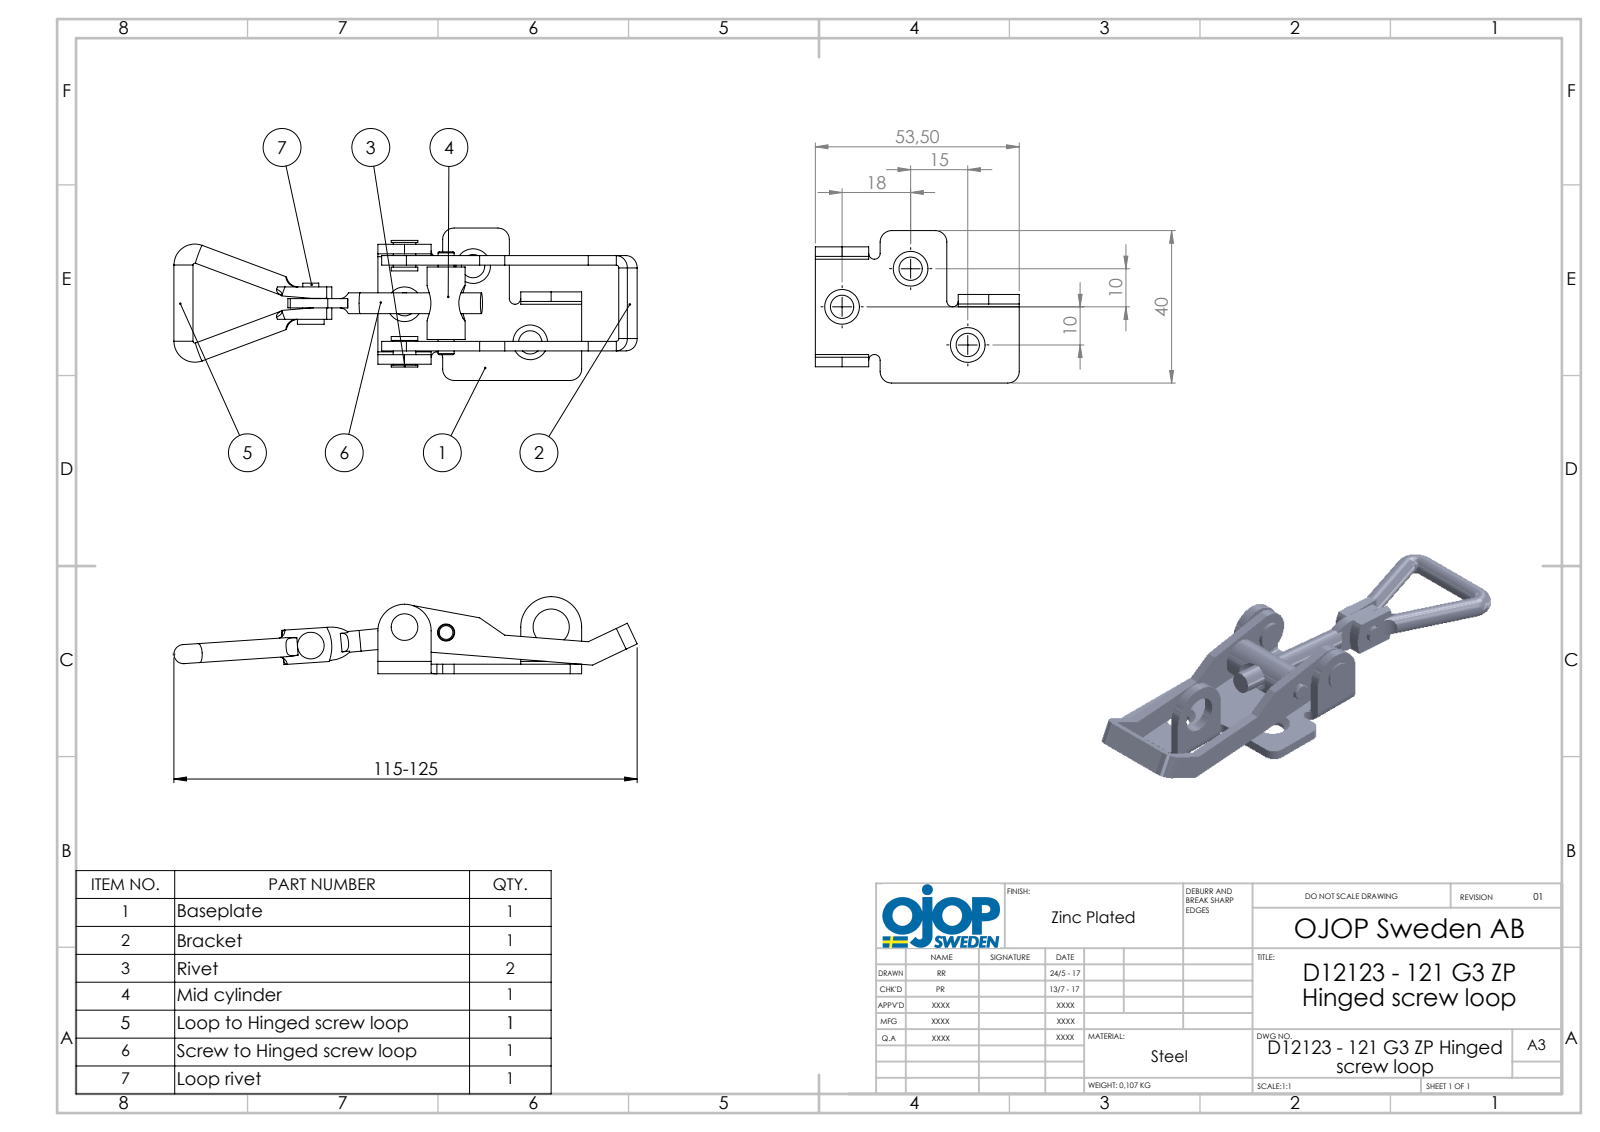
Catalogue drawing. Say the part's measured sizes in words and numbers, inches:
The part is named "bygel; nit; Platta; rulle (+5 more)". Its 3-D file was written by "SolidWorks 2015 (AUTOMOTIVE_DESIGN)". It is 8 solids with 248 faces: 100 planar, 104 cylindrical and 44 other. Overall it measures 4.827 by 1.575 by 0.797 inches. Its volume is 0.836 cubic inches and its surface area 20.86 square inches. Round holes: 3 of diameter 0.217, 3 of diameter 0.236, 2 of diameter 0.177, 1 of diameter 0.197, 1 of diameter 0.374. Round bosses or shafts: 3 of diameter 0.236, 2 of diameter 0.276, 2 of diameter 0.165, 1 of diameter 0.394, 1 of diameter 0.232, 1 of diameter 0.215, 1 of diameter 0.215. Partial cylindrical surfaces (rounded edges, fillets, slot ends): 6 of radius 0.118, 5 of radius 0.029, 5 of radius 0.128, 3 of radius 0.059, 2 of radius 0.079, 2 of radius 0.394, 1 of radius 0.236, 1 of radius 0.276. The main face-to-face distances are 0.098, 0.886, 0.787, 0.984, 0.236, 0.138, 1.141, 0.511, 0.375, 0.648. The hole center spacings are 0.433, 0.811, 0.984, 1.007, 1.068, 1.357, 1.424, 1.496.
